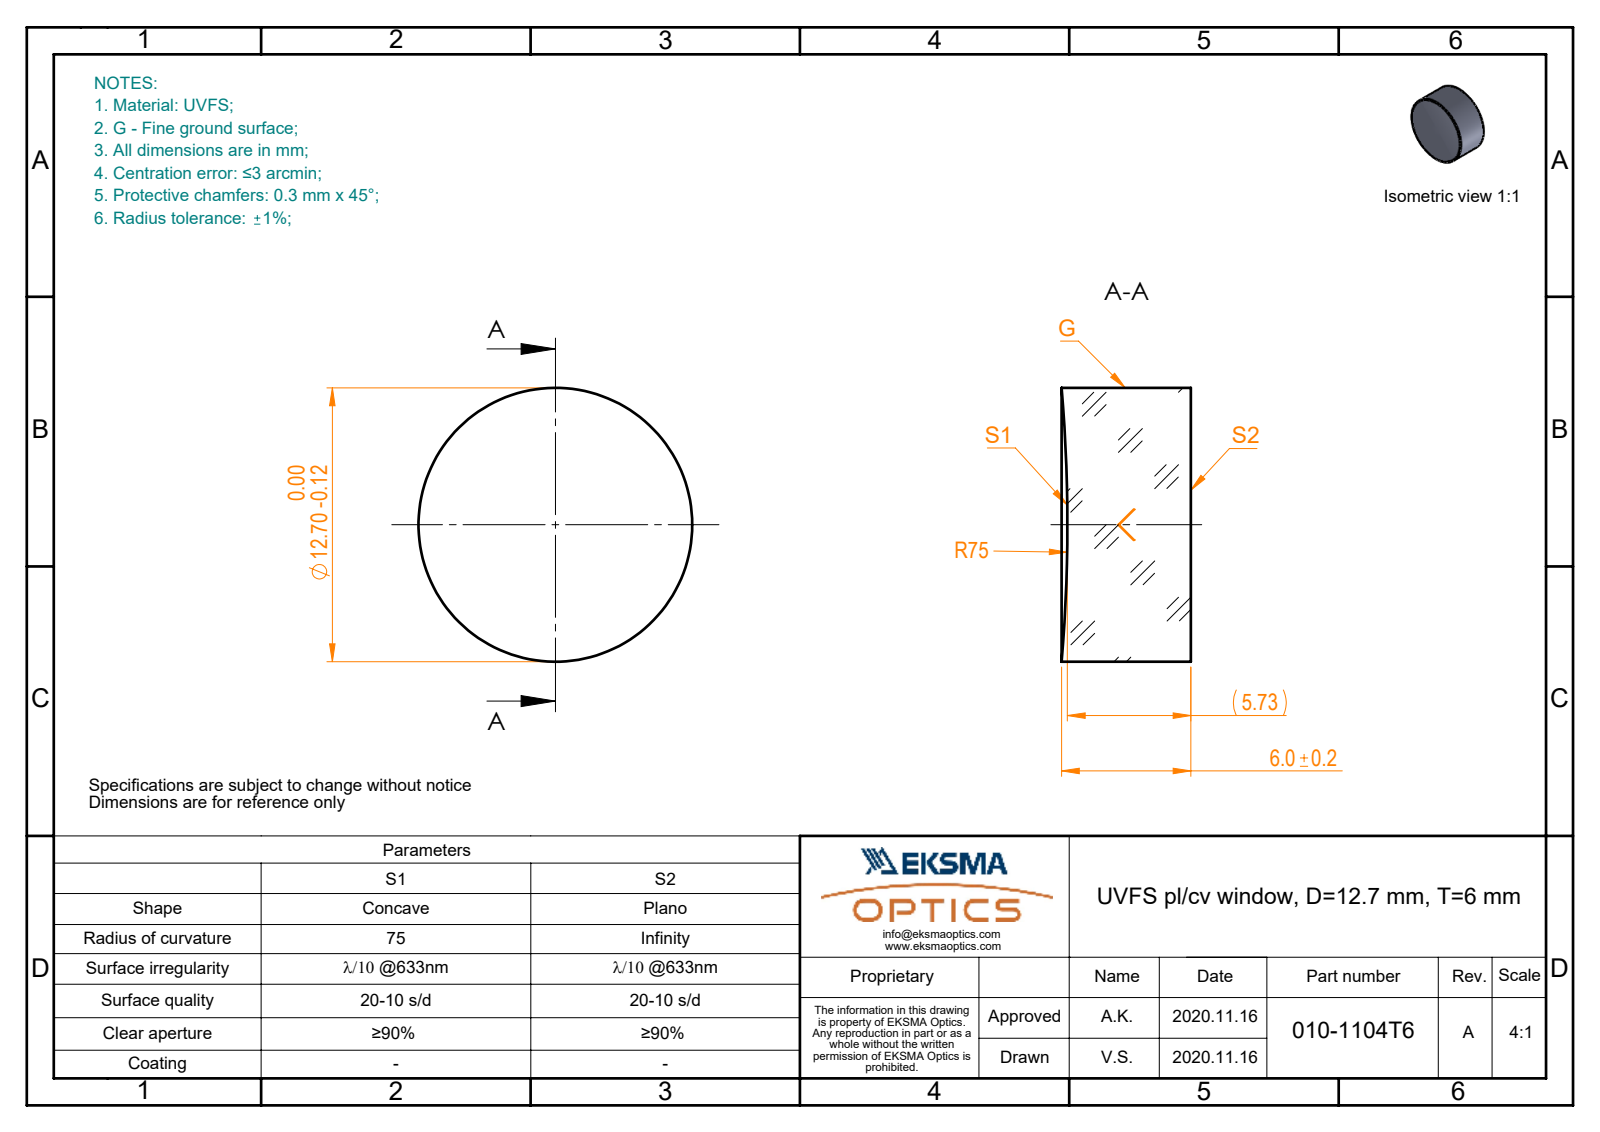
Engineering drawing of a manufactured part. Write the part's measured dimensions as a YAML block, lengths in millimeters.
part_name: "010-1104T6_UVFS_PCV_window"
step_written_by: "SolidWorks 2019 (CONFIG_CONTROL_DESIGN)"
units: millimeters
bodies: {solids: 1, faces: 5, planar: 1, cylindrical: 2, other: 2}
overall_size: [12.7, 12.7, 6]
volume: 743
surface_area: 493
round_bosses_or_shafts:
  - {diameter: 12.7, count: 1}
